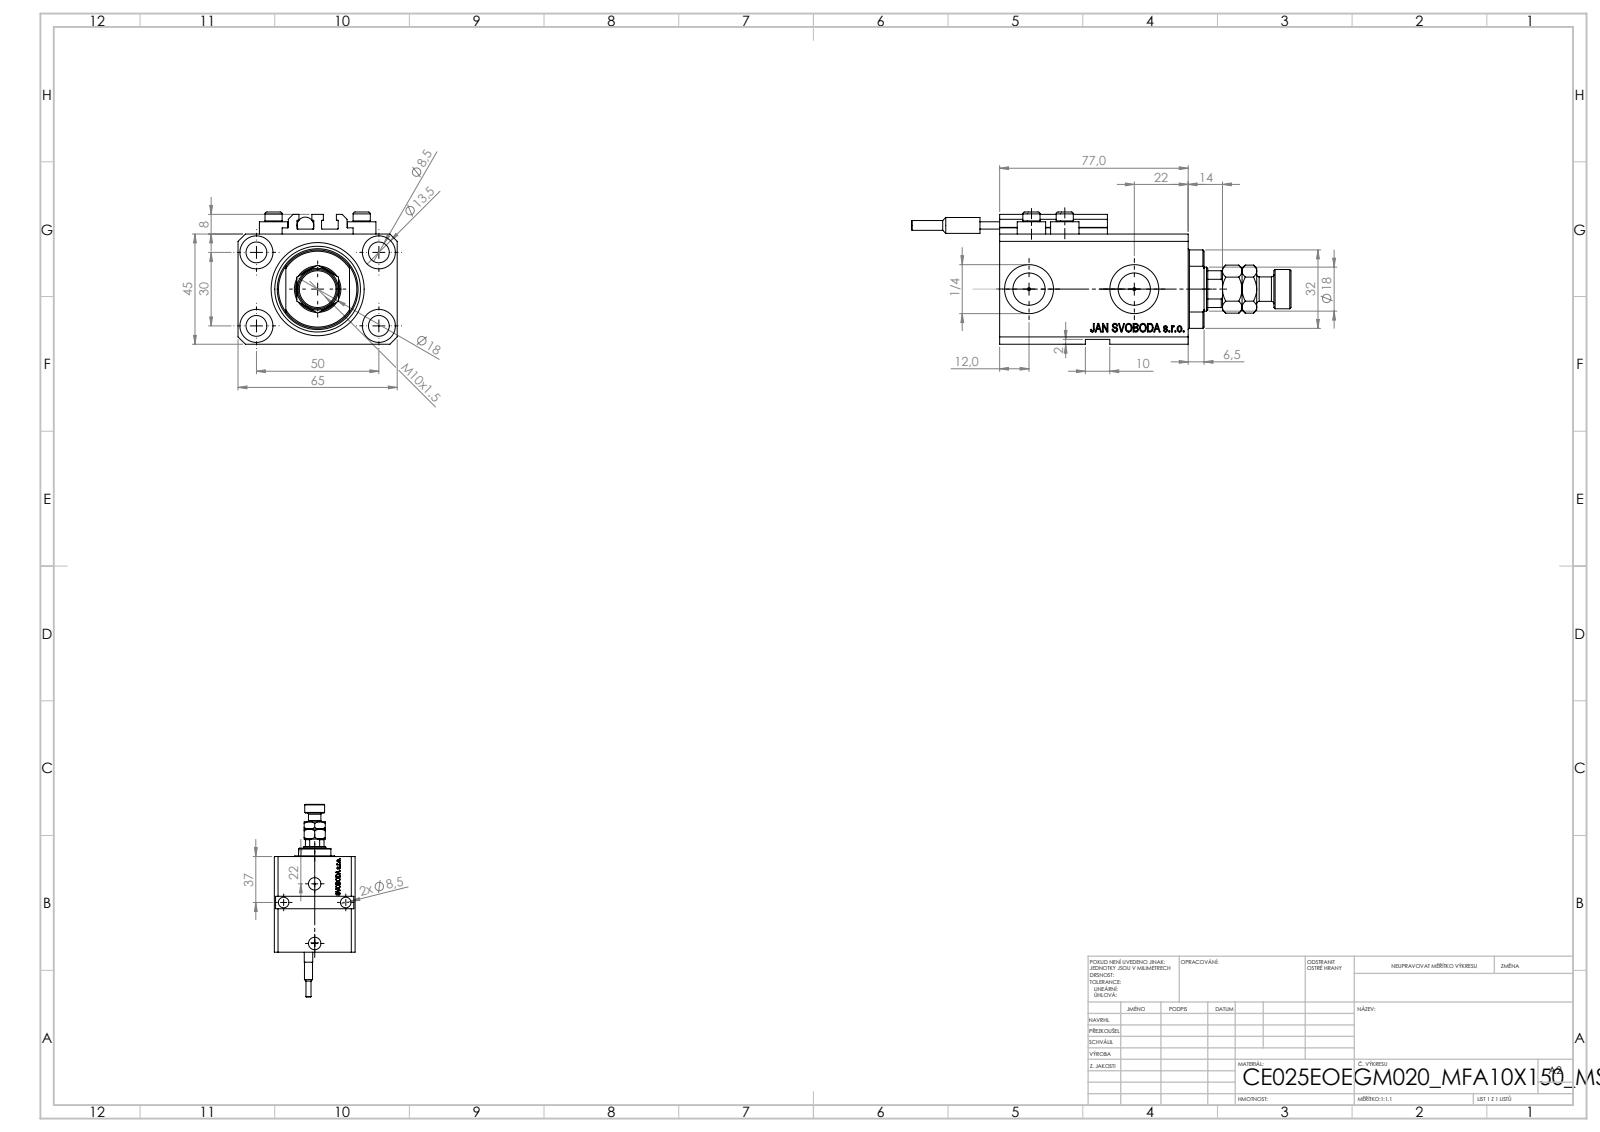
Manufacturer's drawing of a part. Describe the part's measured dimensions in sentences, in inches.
The part is named "ALLEN BOLT V250CE; V250CE_E_Body; V250CE_VC_E; MFA (+2 more)". Its 3-D file was written by "SolidWorks 2019 (CONFIG_CONTROL_DESIGN)". It is 10 solids with 1145 faces: 543 planar, 136 cylindrical and 466 other. Overall it measures 6.102 by 2.559 by 2.126 inches. Its volume is 12.63 cubic inches and its surface area 97.07 square inches. Round holes: 7 of diameter 0.335, 4 of diameter 0.049, 4 of diameter 0.157, 4 of diameter 0.531, 2 of diameter 0.394, 2 of diameter 0.518, 2 of diameter 0.787, 1 of diameter 0.709, 1 of diameter 0.984, 1 of diameter 1.496. Round bosses or shafts: 4 of diameter 0.457, 4 of diameter 0.276, 1 of diameter 0.63, 1 of diameter 0.394, 1 of diameter 0.268, 1 of diameter 0.256, 1 of diameter 0.157. Partial cylindrical surfaces (rounded edges, fillets, slot ends): 10 of radius 0.008, 1 of radius 0.335, 1 of radius 0.63. The main face-to-face distances are 1.772, 2.559, 0.551, 2.48, 3.031, 0.079, 0.272, 0.118, 1.85, 0.197. The hole center spacings are 1.148, 1.969, 0.535, 0.595, 0.741, 0.747, 1.032, 1.048.
